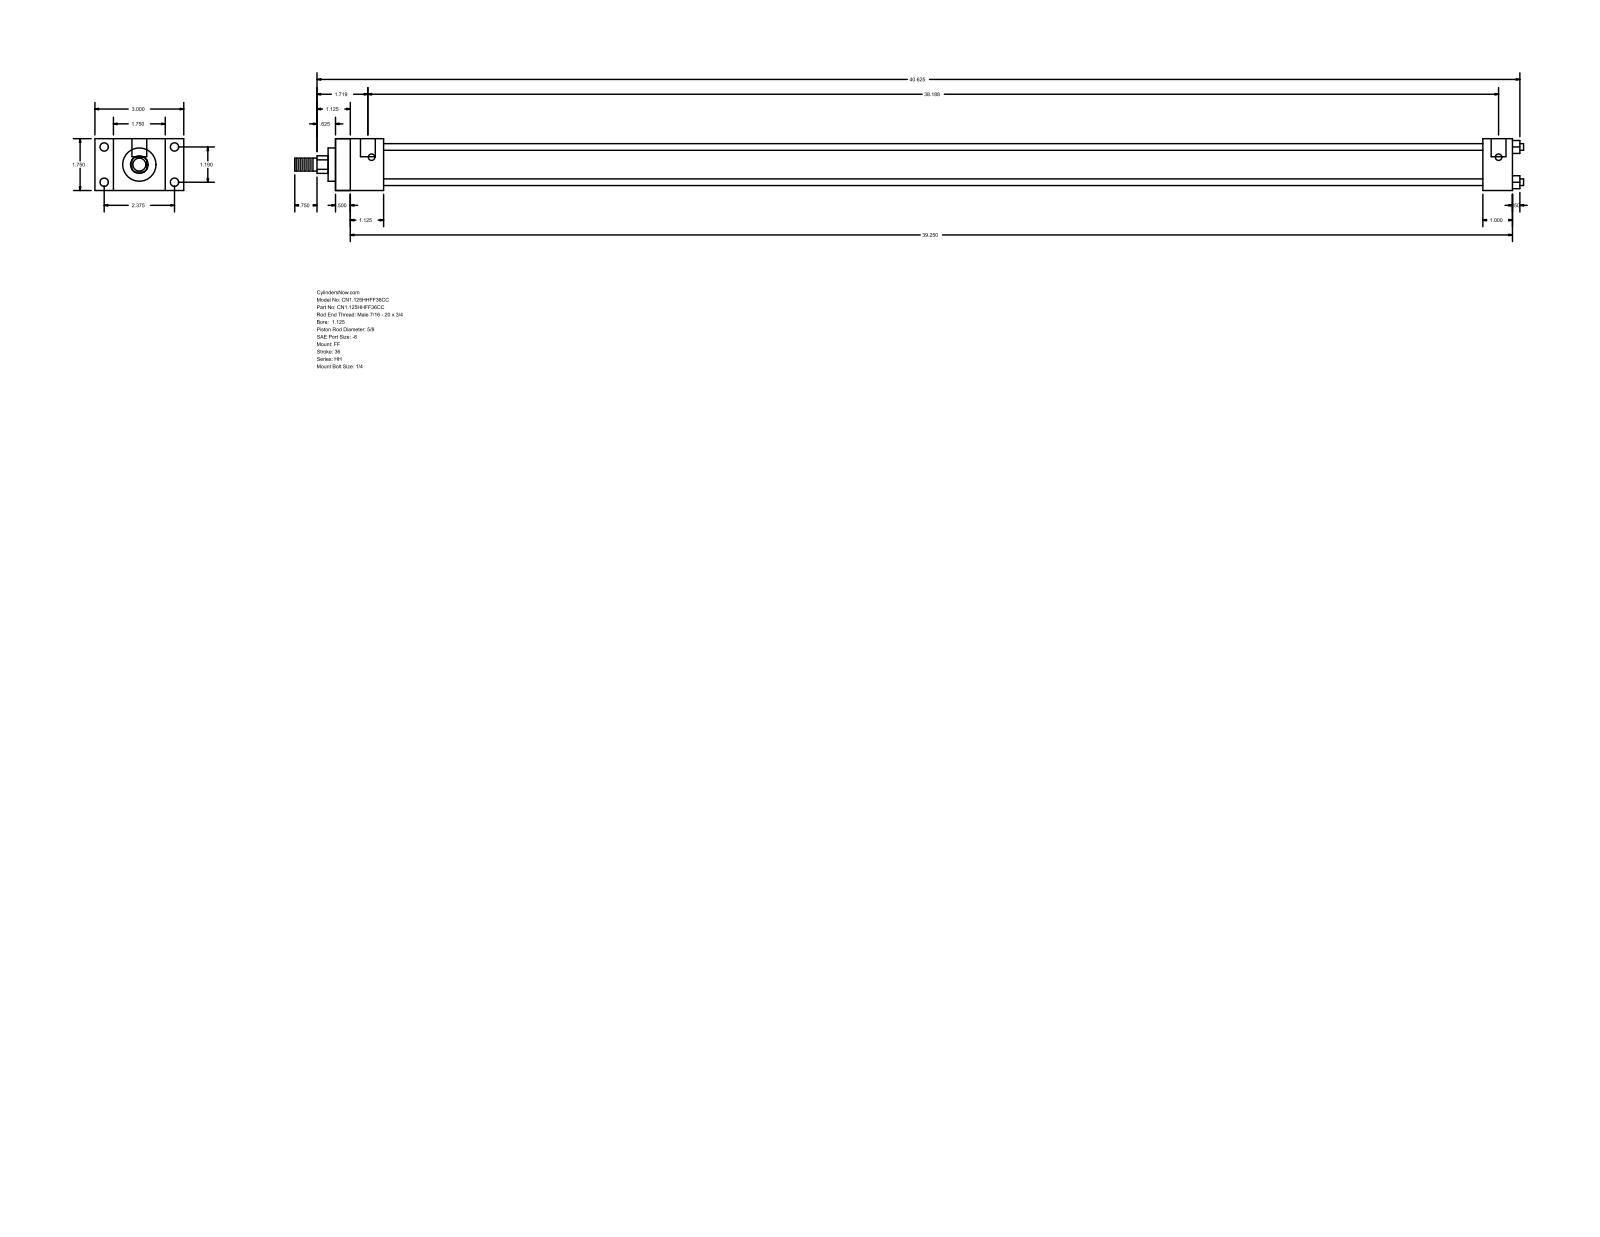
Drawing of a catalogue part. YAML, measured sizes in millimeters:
part_name: "HH_FF__0112_0.625"
step_written_by: "GSSL Pune (CONFIG_CONTROL_DESIGN)"
units: millimeters
bodies: {solids: 0, faces: 92, planar: 64, cylindrical: 28, other: 0}
overall_size: [1054.1, 76.2, 44.45]
round_holes:
  - {diameter: 5.56, count: 4}
  - {diameter: 7.14, count: 4}
  - {diameter: 12.7, count: 2}
round_bosses_or_shafts:
  - {diameter: 5.71, count: 4}
  - {diameter: 34.92, count: 1}
  - {diameter: 28.57, count: 1}
  - {diameter: 15.88, count: 1}
  - {diameter: 11.11, count: 1}
partial_cylinders:
  - {radius: 7.54, count: 1}
face_to_face_distances: [44.46, 1009.65, 12.69, 996.96, 15.87, 28.58, 60.33, 41.27, 984.24, 971.55]
hole_center_spacings: [30.22, 60.32, 67.47, 966.79, 3.17, 969.96]
